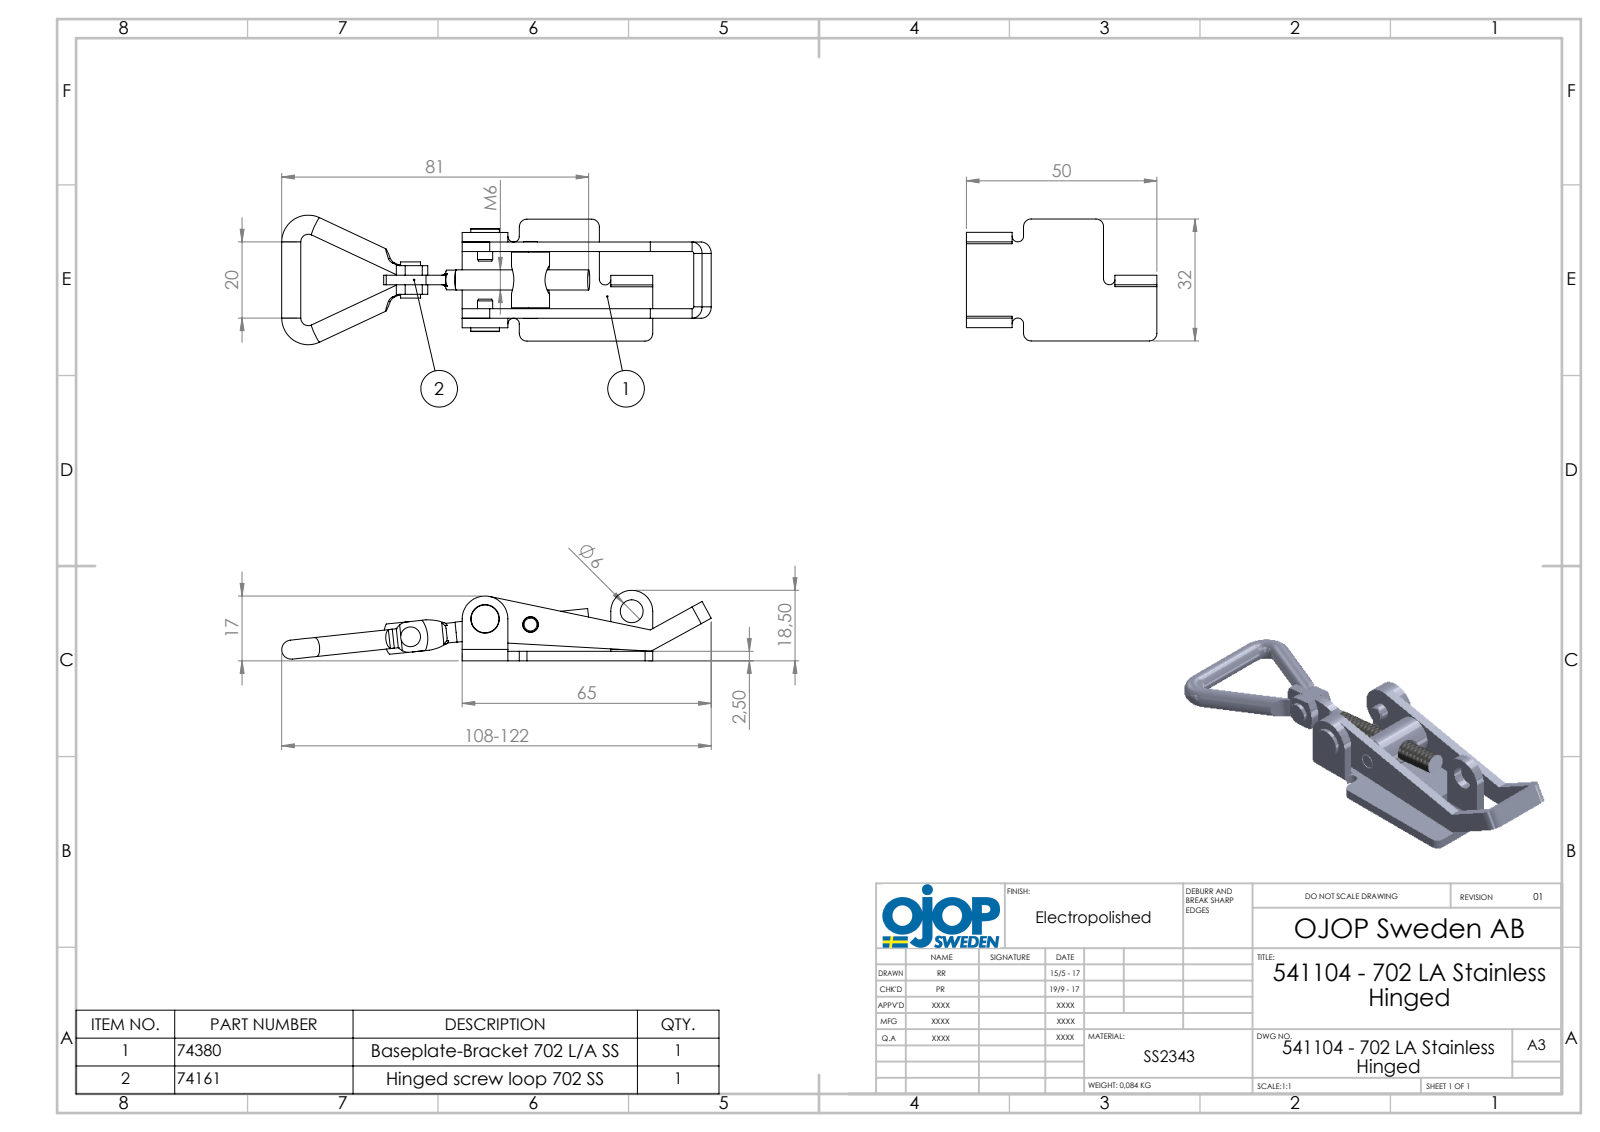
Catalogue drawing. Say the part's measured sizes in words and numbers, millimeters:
The part is named "702 - Bygel; 702 - Platta LA; 702 - Skruv till ledad M6; 702 - Rulle (+5 more)". Its 3-D file was written by "SolidWorks 2015 (AUTOMOTIVE_DESIGN)". It is 8 solids with 216 faces: 90 planar, 104 cylindrical and 22 other. Overall it measures 115.58 by 34 by 18.5 millimeters. Its volume is 11 235 cubic millimeters and its surface area 11 193 square millimeters. Round holes: 3 of diameter 4.1, 2 of diameter 6, 1 of diameter 5. Round bosses or shafts: 3 of diameter 5, 2 of diameter 4, 1 of diameter 10, 1 of diameter 7.5, 1 of diameter 5.3, 1 of diameter 5.2, 1 of diameter 5.18. Partial cylindrical surfaces (rounded edges, fillets, slot ends): 8 of radius 2, 6 of radius 1, 5 of radius 0.5, 5 of radius 3, 2 of radius 1.5, 2 of radius 6.78, 2 of radius 12.31, 1 of radius 1.51. The main face-to-face distances are 2.5, 17.5, 20, 8.75, 11.25, 15, 5, 8.8, 8.7, 11.3. The hole center spacings are 12.02, 22.82, 26.8, 34.43, 38.55, 61.21.
